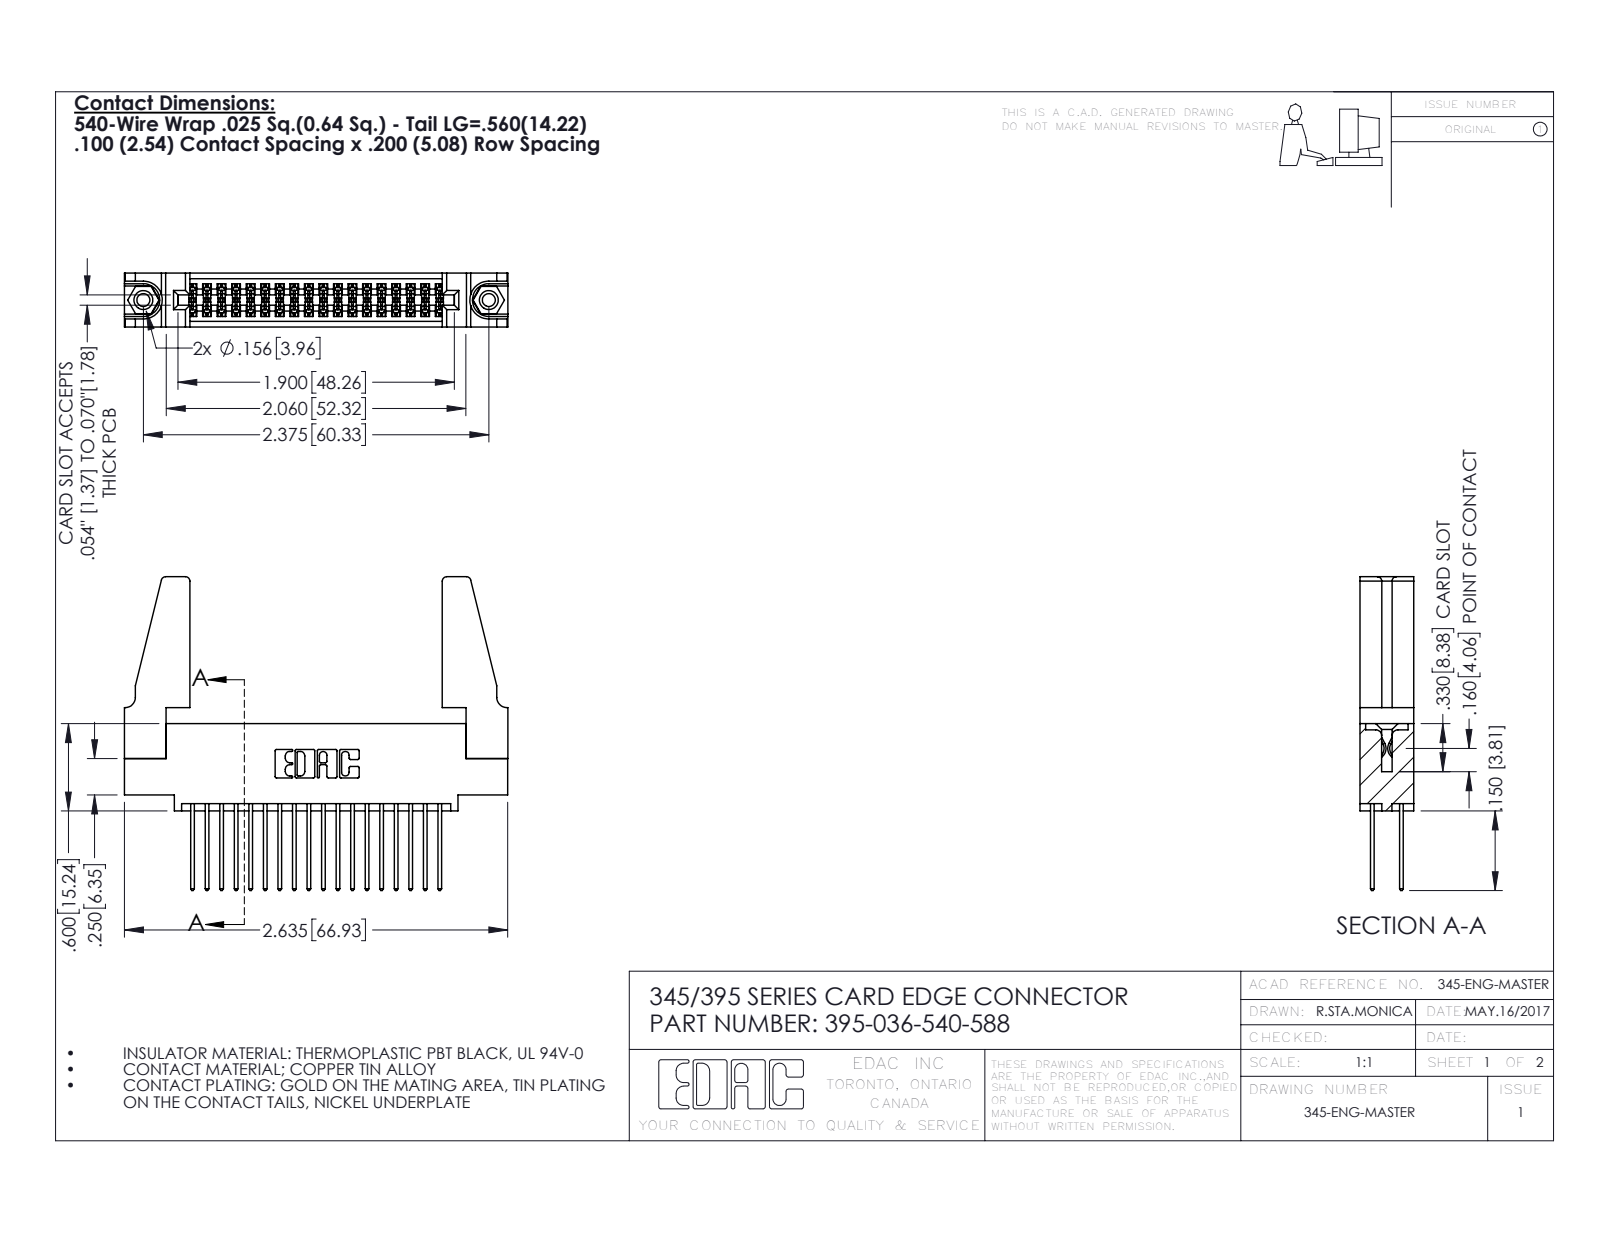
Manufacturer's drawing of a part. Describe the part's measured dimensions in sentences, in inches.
The part is named "345-220-078_345-220-088; 345-250-001_345-250-001-102; 345 Part_0.110 Offset - 0.156 Dia-TH; 345-292-001_345-293-140 (+1 more)". Its 3-D file was written by "SolidWorks 2016 (CONFIG_CONTROL_DESIGN)". It is 41 solids with 2054 faces: 1344 planar, 694 cylindrical and 16 other. Overall it measures 2.636 by 2.157 by 0.37 inches. Its volume is 0.586 cubic inches and its surface area 19.78 square inches. Round holes: 2 of diameter 0.089, 2 of diameter 0.125, 2 of diameter 0.156, 1 of diameter 0.064. Round bosses or shafts: 2 of diameter 0.155. Partial cylindrical surfaces (rounded edges, fillets, slot ends): 54 of radius 0.006, 36 of radius 0.01, 22 of radius 0.01, 8 of radius 0.03, 6 of radius 0.007, 6 of radius 0.031, 3 of radius 0.026, 2 of radius 0.014. The main face-to-face distances are 0.072, 0.298, 0.37, 0.2, 0.098, 0.272, 0.025, 0.225, 0.175, 0.15. The hole center spacings are 0.27, 2.141, 2.375.
